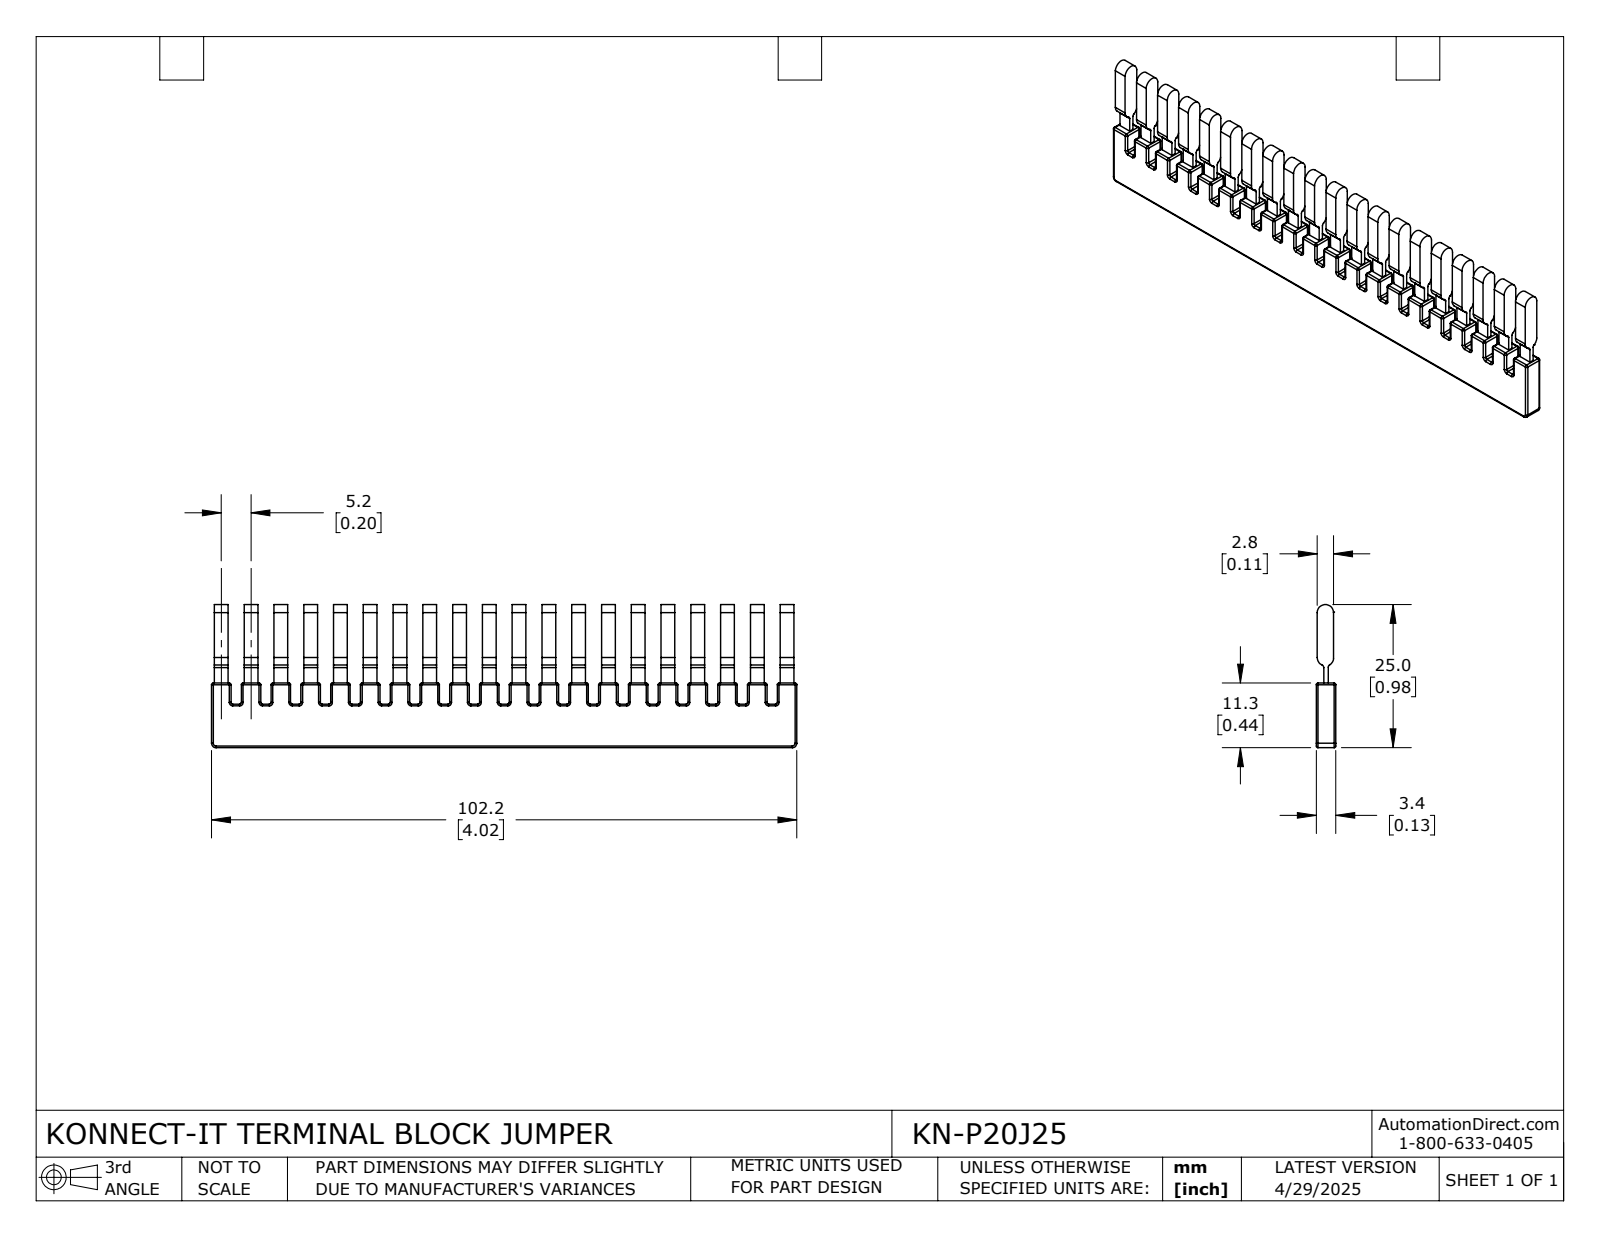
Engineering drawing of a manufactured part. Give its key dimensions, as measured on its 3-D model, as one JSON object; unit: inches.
{"part_name": "KN-P20J25", "step_written_by": "SolidWorks 2024 (CONFIG_CONTROL_DESIGN)", "units": "inches", "bodies": {"solids": 1, "faces": 752, "planar": 233, "cylindrical": 359, "other": 160}, "overall_size": [4.024, 0.984, 0.134], "volume_in3": 0.304, "surface_area_in2": 9.018, "partial_cylinders_radius": [[0.012, 164], [0.079, 10], [0.02, 2], [0.031, 2], [0.056, 2], [0.051, 1]], "face_to_face_distances": [0.134, 0.205, 0.409, 0.614, 0.819, 1.024, 1.228, 1.433, 0.015, 0.119]}
